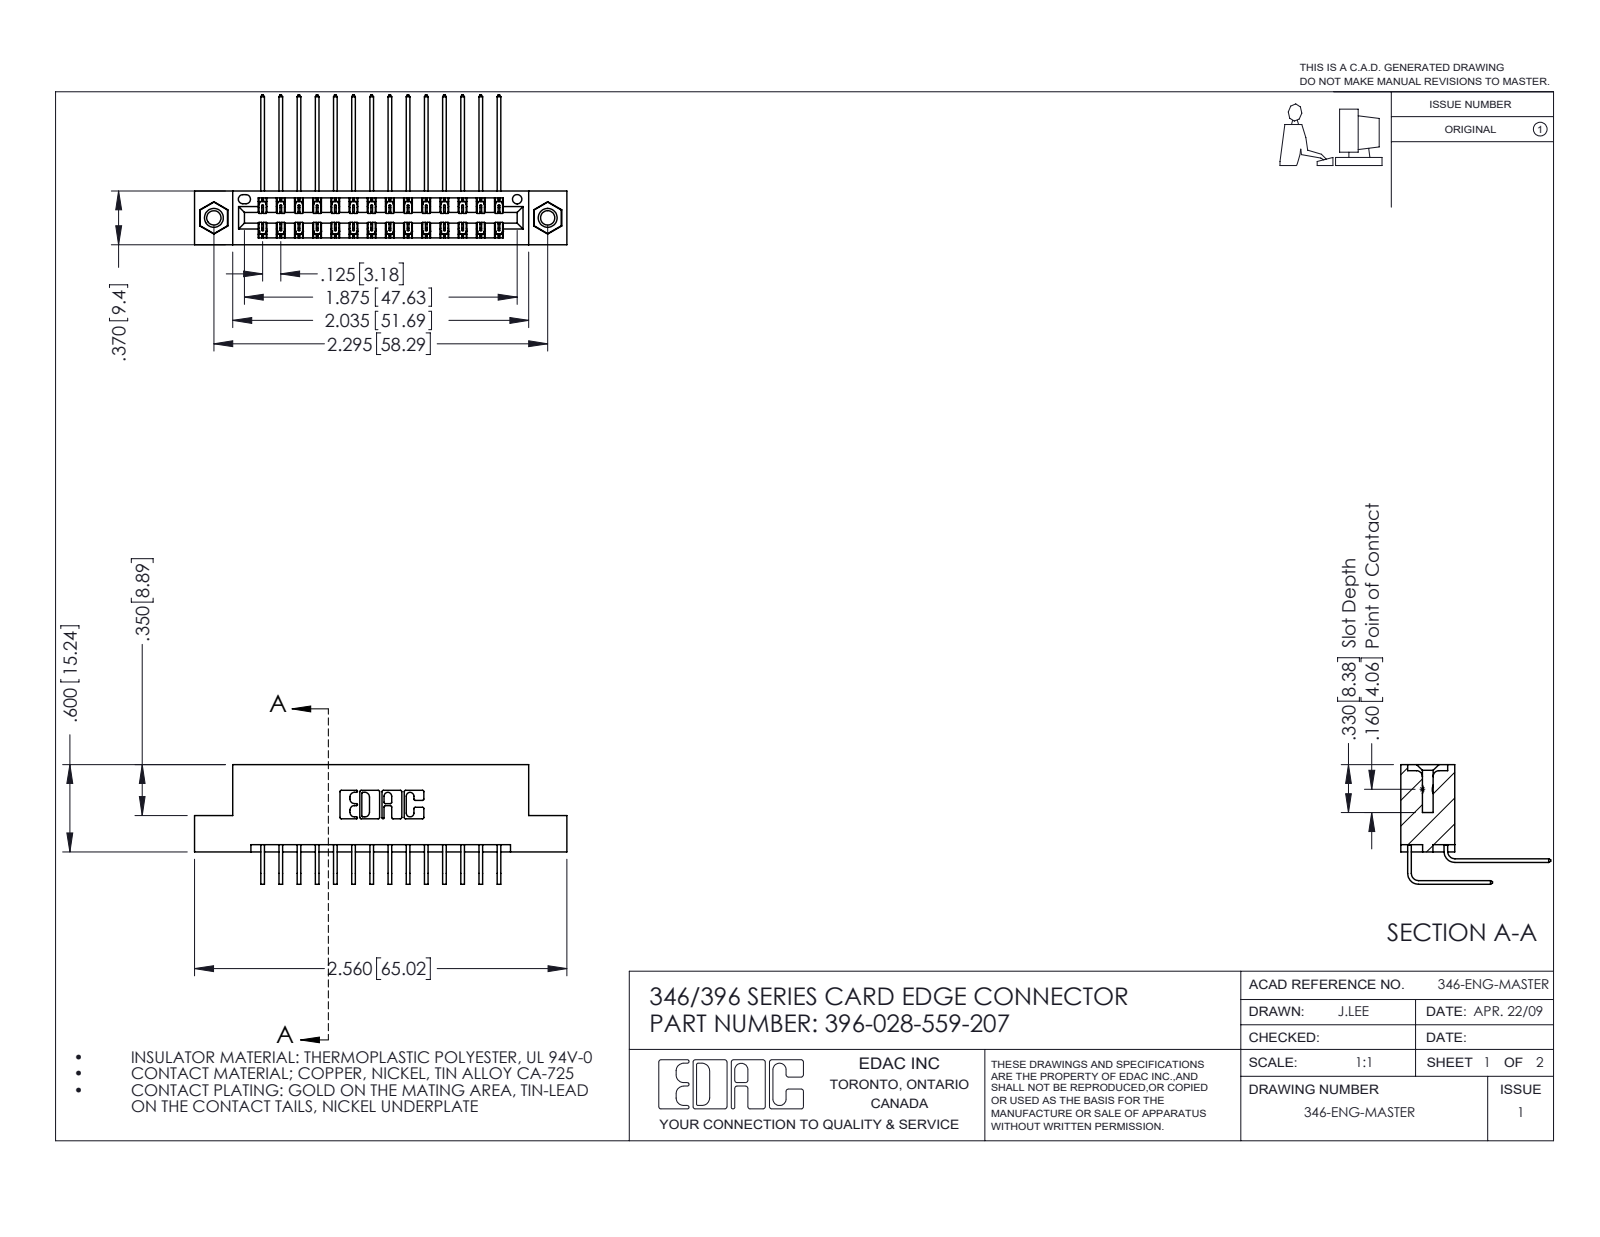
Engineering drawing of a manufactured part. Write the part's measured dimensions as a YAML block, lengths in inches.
part_name: "346 Part_Flush Mounting Lugs - 0.156 Dia-TI; 345-292-001_558 559 Tail - 1; 396-028-559-207; 345-250-001_345-250-005-103 (+1 more)"
step_written_by: "SolidWorks 2016 (CONFIG_CONTROL_DESIGN)"
units: inches
bodies: {solids: 31, faces: 1694, planar: 1144, cylindrical: 534, other: 16}
overall_size: [2.56, 1.03, 0.823]
volume: 0.383
surface_area: 13.93
round_holes:
  - {diameter: 0.098, count: 2}
  - {diameter: 0.125, count: 2}
  - {diameter: 0.156, count: 2}
  - {diameter: 0.064, count: 1}
round_bosses_or_shafts:
  - {diameter: 0.155, count: 2}
partial_cylinders:
  - {radius: 0.006, count: 42}
  - {radius: 0.01, count: 22}
  - {radius: 0.007, count: 6}
  - {radius: 0.031, count: 6}
  - {radius: 0.026, count: 3}
  - {radius: 0.014, count: 2}
  - {radius: 0.022, count: 2}
  - {radius: 0.024, count: 2}
face_to_face_distances: [0.048, 0.322, 0.25, 0.37, 0.025, 0.072, 0.298, 0.275, 0.148, 0.222]
hole_center_spacings: [0.246, 2.089, 2.295]
